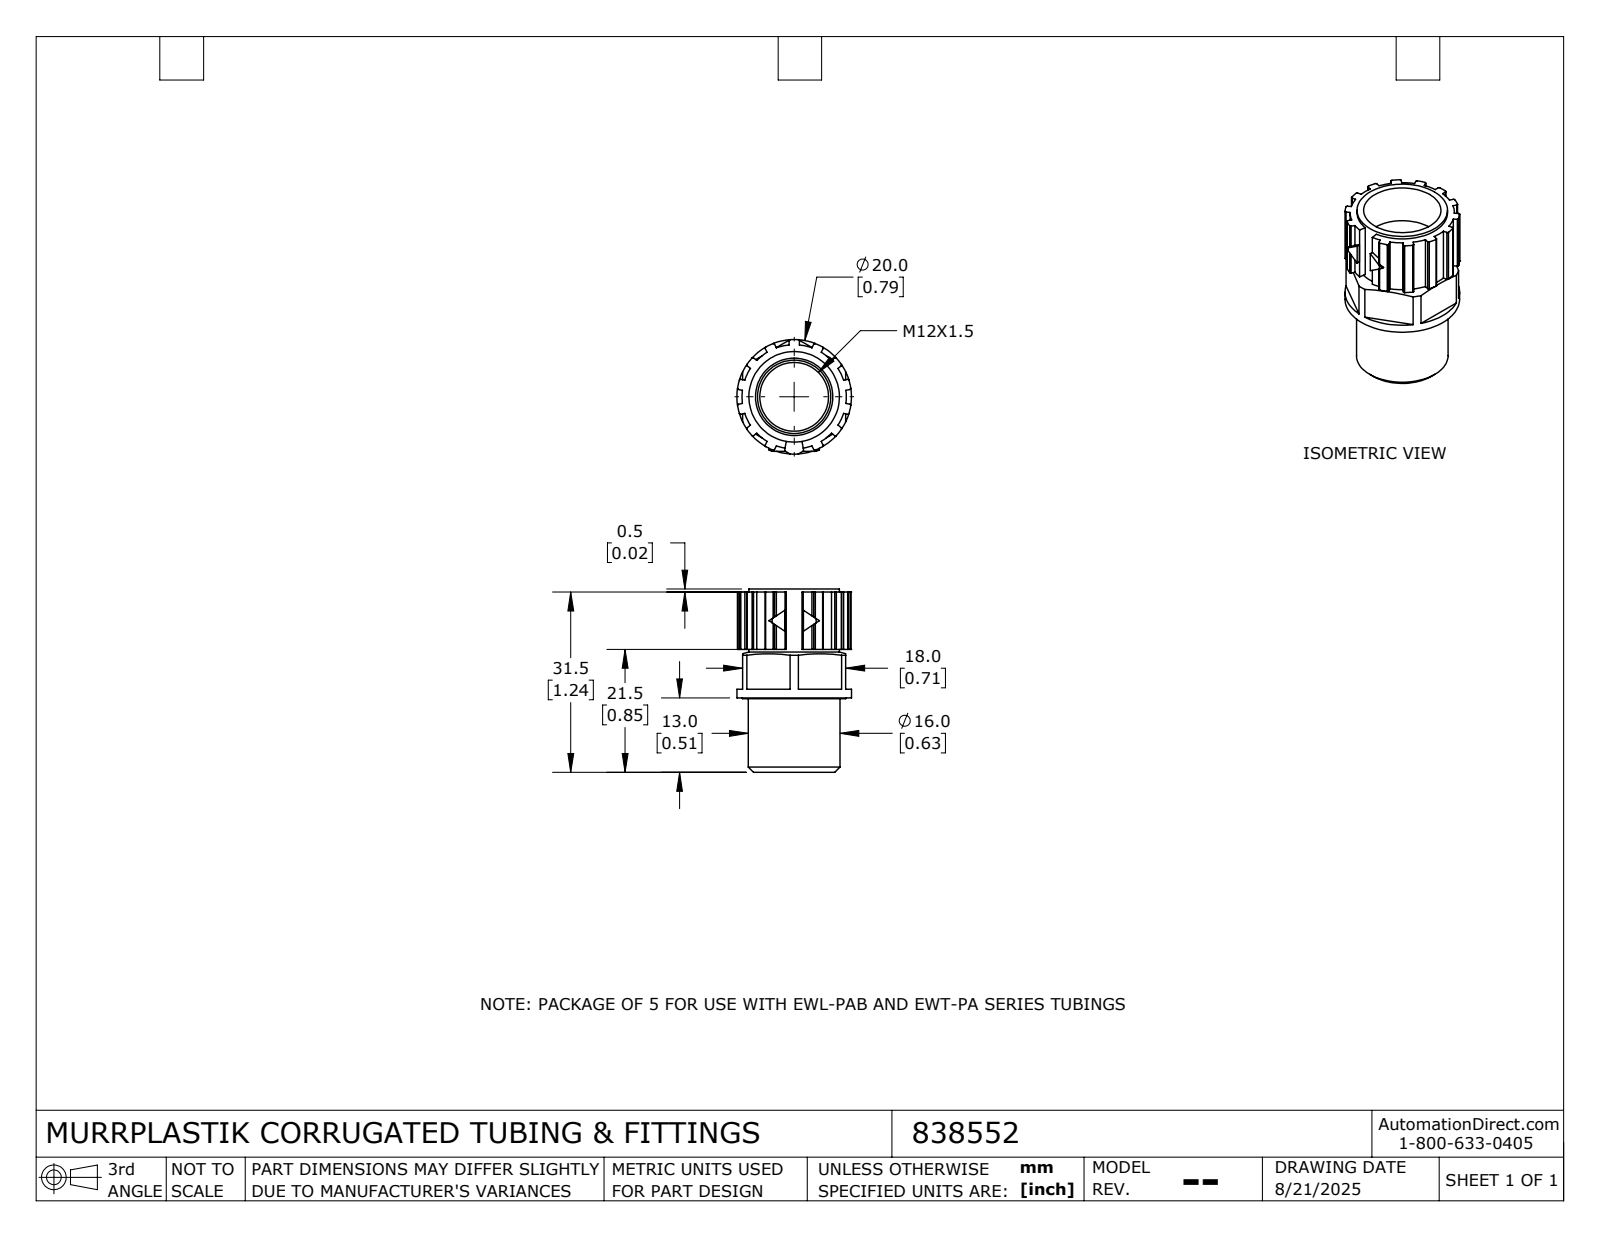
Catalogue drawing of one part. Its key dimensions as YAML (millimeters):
part_name: "838552_Default"
step_written_by: "SolidWorks 2024 (CONFIG_CONTROL_DESIGN)"
units: millimeters
bodies: {solids: 1, faces: 125, planar: 57, cylindrical: 63, other: 5}
overall_size: [32, 20, 20]
volume: 3813
surface_area: 3791
round_holes:
  - {diameter: 12, count: 1}
  - {diameter: 12.8, count: 1}
  - {diameter: 13.5, count: 1}
round_bosses_or_shafts:
  - {diameter: 20, count: 1}
  - {diameter: 16, count: 1}
  - {diameter: 15.8, count: 1}
partial_cylinders:
  - {radius: 0.2, count: 26}
  - {radius: 9.1, count: 1}
  - {radius: 10.25, count: 1}
face_to_face_distances: [18, 1.8, 8.47, 10, 18.47, 0.53, 10.53, 19, 17.5, 16.97]
